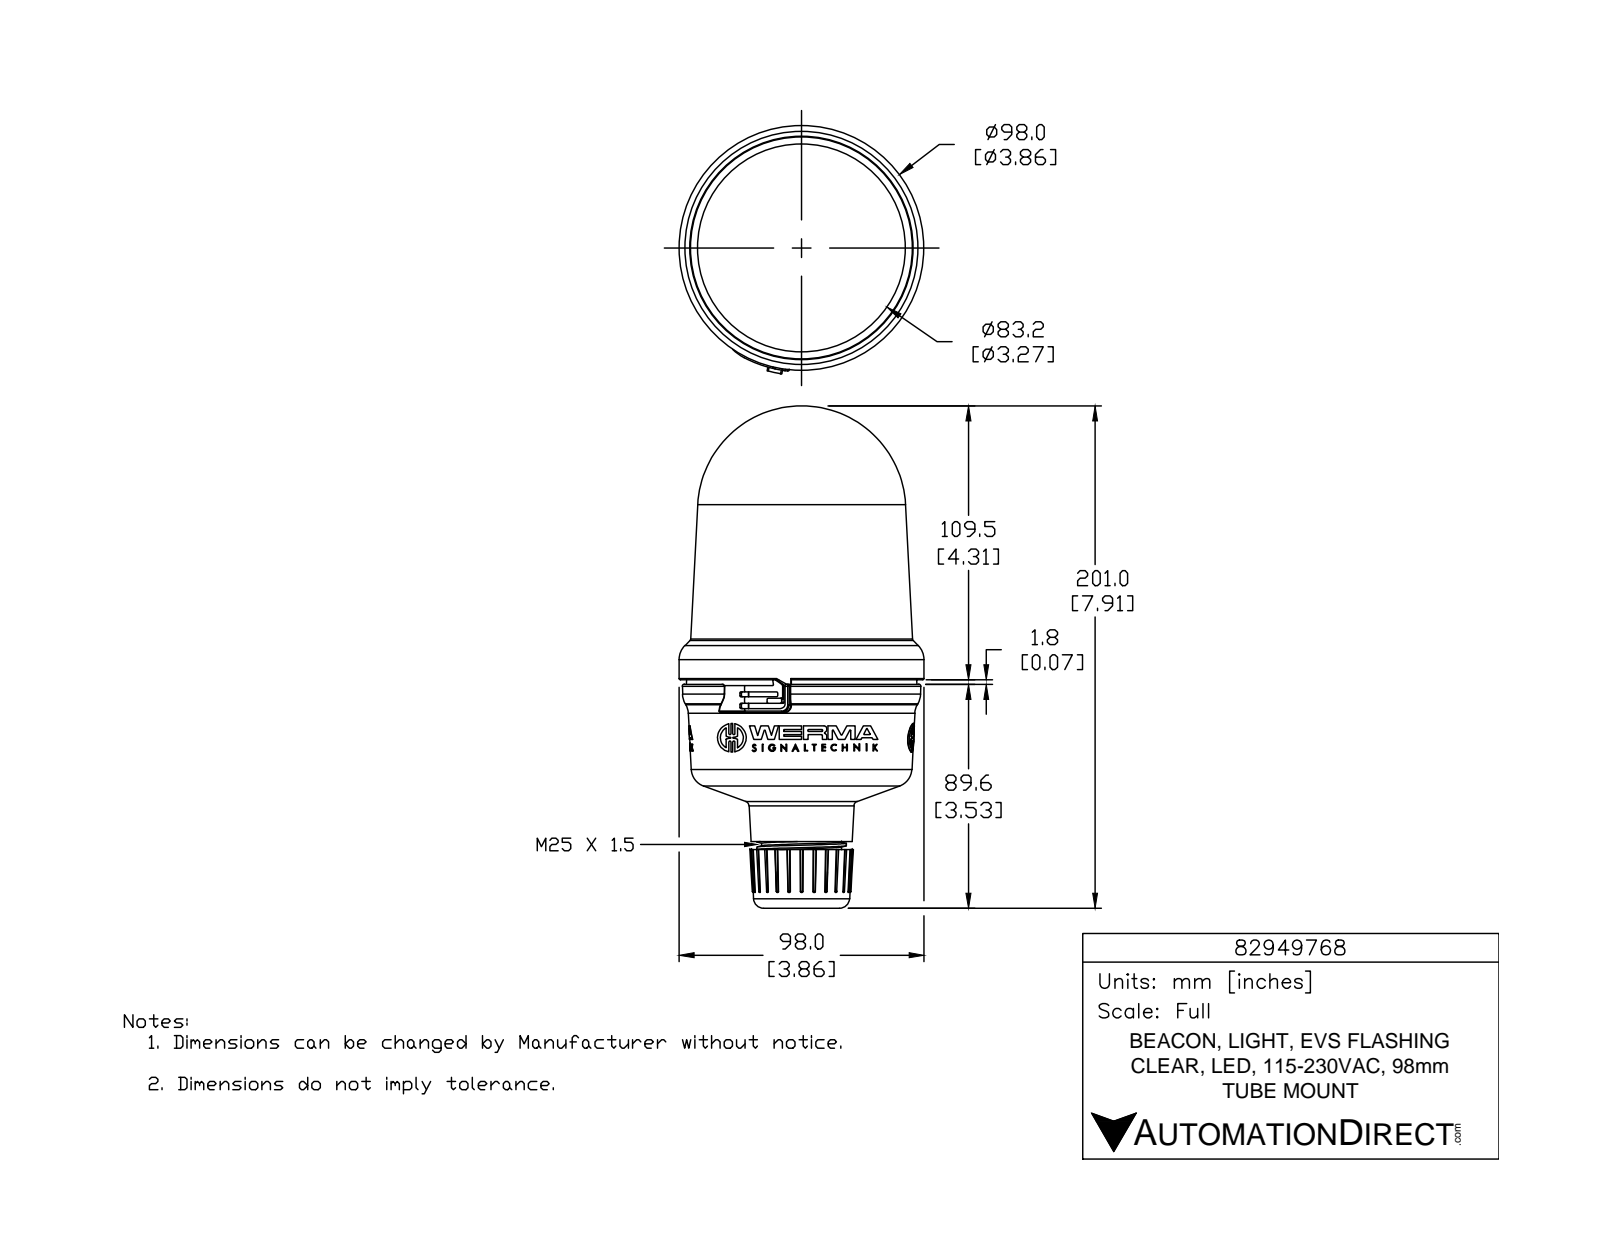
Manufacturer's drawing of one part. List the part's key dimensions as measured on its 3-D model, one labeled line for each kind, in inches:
Part name (STEP PRODUCT): 82949768
STEP written by: SolidWorks 2015 (AUTOMOTIVE_DESIGN)
Units: inches
Bodies: 1 solid, 1006 faces (554 planar, 189 cylindrical, 263 other)
Overall size (bounding box): 7.914 × 3.912 × 3.858
Volume: 54.7 in³ · Surface area: 91.39 in²
Round holes (diameter × count): ⌀0.078 ×3, ⌀1.013 ×1, ⌀1.024 ×1
Round bosses / shafts (diameter × count): ⌀0.452 ×3, ⌀0.113 ×3, ⌀3.858 ×1, ⌀1.409 ×1, ⌀1.261 ×1
Partial cylindrical surfaces — rounded edges, fillets, slot ends (radius × count): R0.02 ×12, R0.007 ×9, R0.007 ×6, R0.016 ×6, R0.016 ×6, R0.016 ×6, R0.262 ×6, R0.006 ×3
Main face-to-face distances: 2.214, 0.462, 2.676, 0.335, 0.127, 2.548, 2.603, 2.476, 2.141, 0.073
